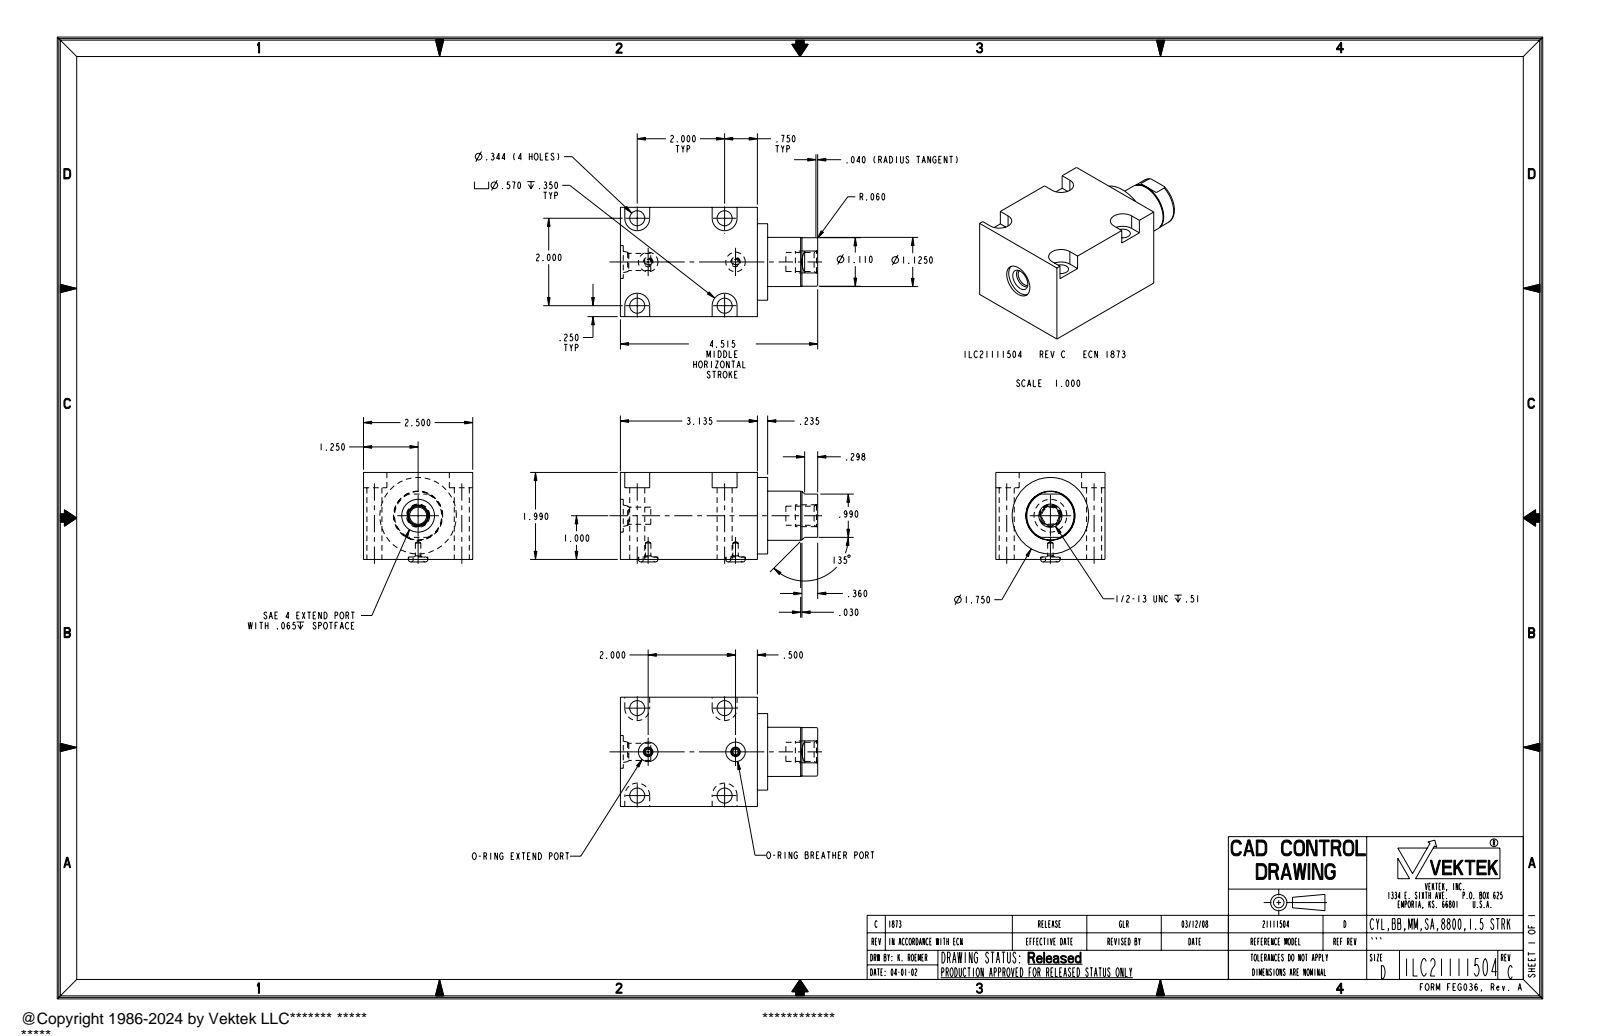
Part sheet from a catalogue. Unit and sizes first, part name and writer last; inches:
Units: inches
Overall size (bounding box): 4.515 × 2.5 × 2.047
Round holes (diameter × count): ⌀0.344 ×4, ⌀0.125 ×2, ⌀0.447 ×2, ⌀0.392 ×1, ⌀0.437 ×1, ⌀0.75 ×1
Round bosses / shafts (diameter × count): ⌀1.75 ×1, ⌀1.125 ×1, ⌀1.11 ×1, ⌀0.5 ×1
Partial cylindrical surfaces — rounded edges, fillets, slot ends (radius × count): R0.285 ×4
Main face-to-face distances: 1.99, 2.5, 3.135, 0.235, 3.37, 1.64, 0.35, 1.145, 1.38, 4.515
Hole centre spacings: 2, 1.031, 2.016, 2.462, 2.828
Volume: 16.06 in³ · Surface area: 54.66 in²
Bodies: 1 solid, 90 faces (30 planar, 34 cylindrical, 26 other)
Part name (STEP PRODUCT): ILC21111504
STEP written by: PRO/ENGINEER BY PARAMETRIC TECHNOLOGY CORPORATION, 2007460 (AUTOMOTIVE_DESIGN_CC2)
